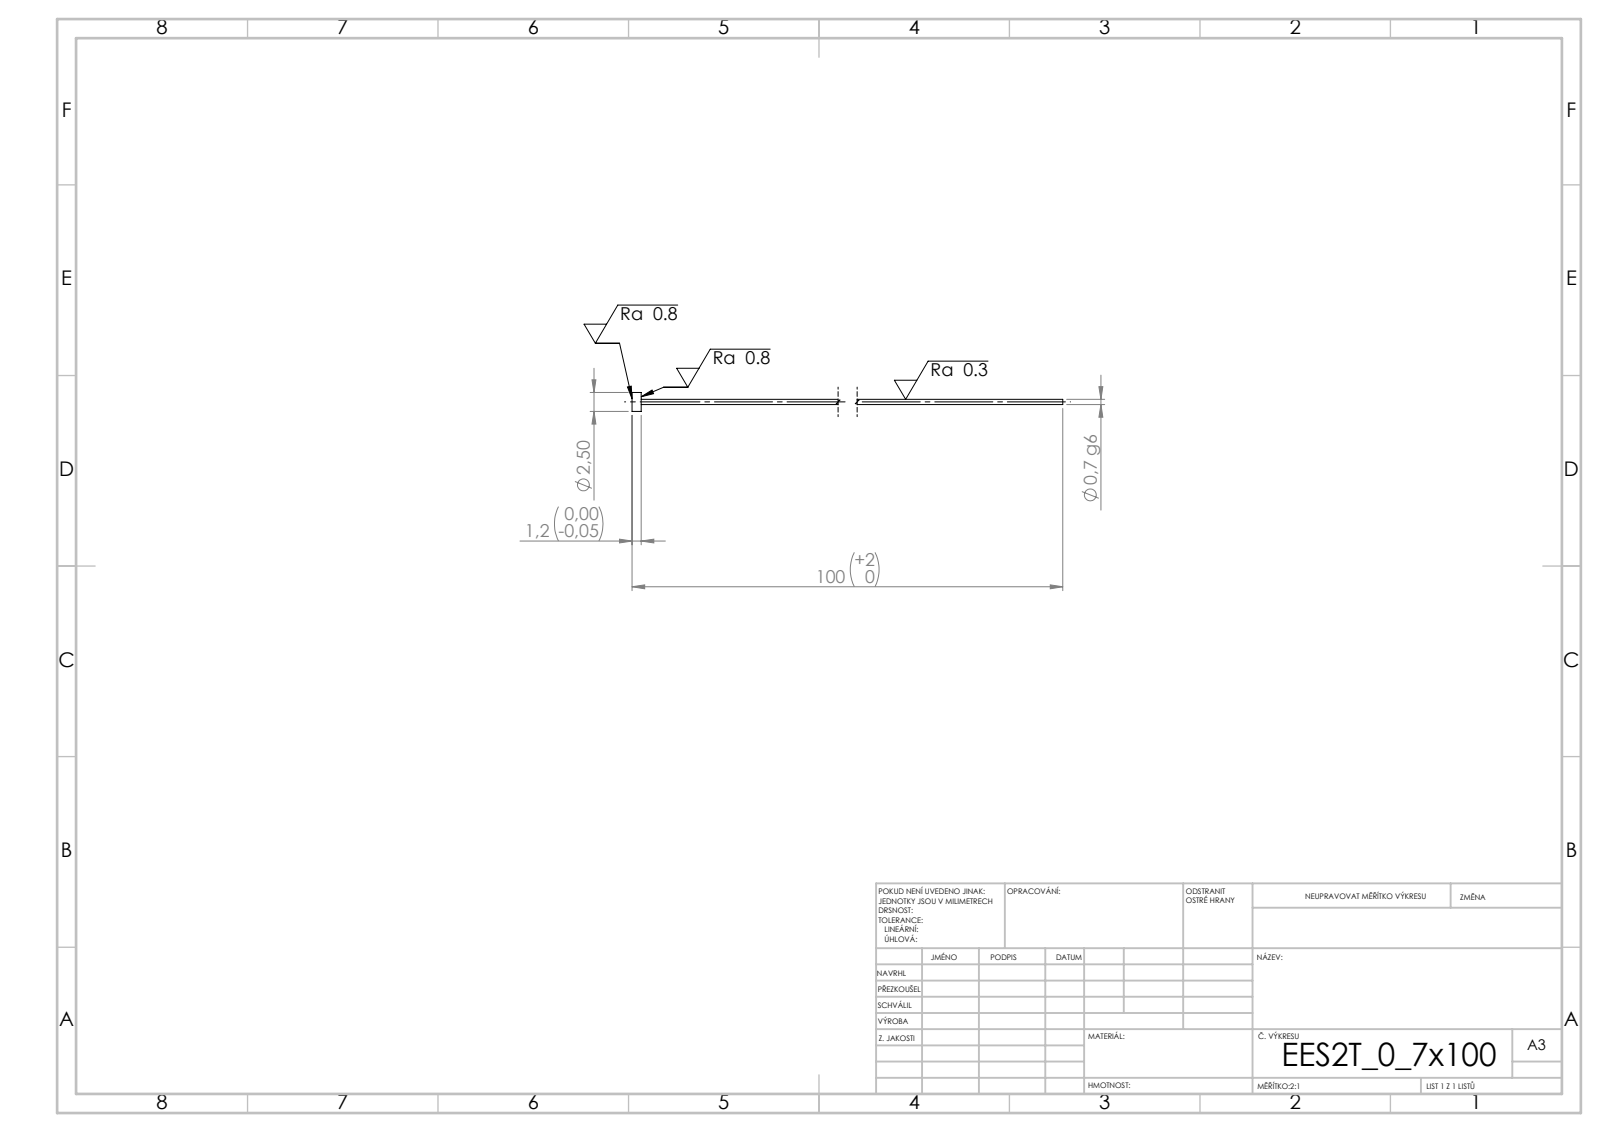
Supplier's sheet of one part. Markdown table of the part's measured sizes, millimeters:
| quantity | value |
| --- | --- |
| STEP written by | SolidWorks 2019 (CONFIG_CONTROL_DESIGN) |
| units | millimeters |
| bodies | 1 solid, 7 faces (3 planar, 4 cylindrical, 0 other) |
| overall size | 100 × 2.5 × 2.5 |
| volume | 44 mm³ |
| surface area | 237 mm² |
| round bosses / shafts (diameter × count) | 2.5 × 1, 0.7 × 1 |
| main face-to-face distances | 1.2, 100, 98.8 |
